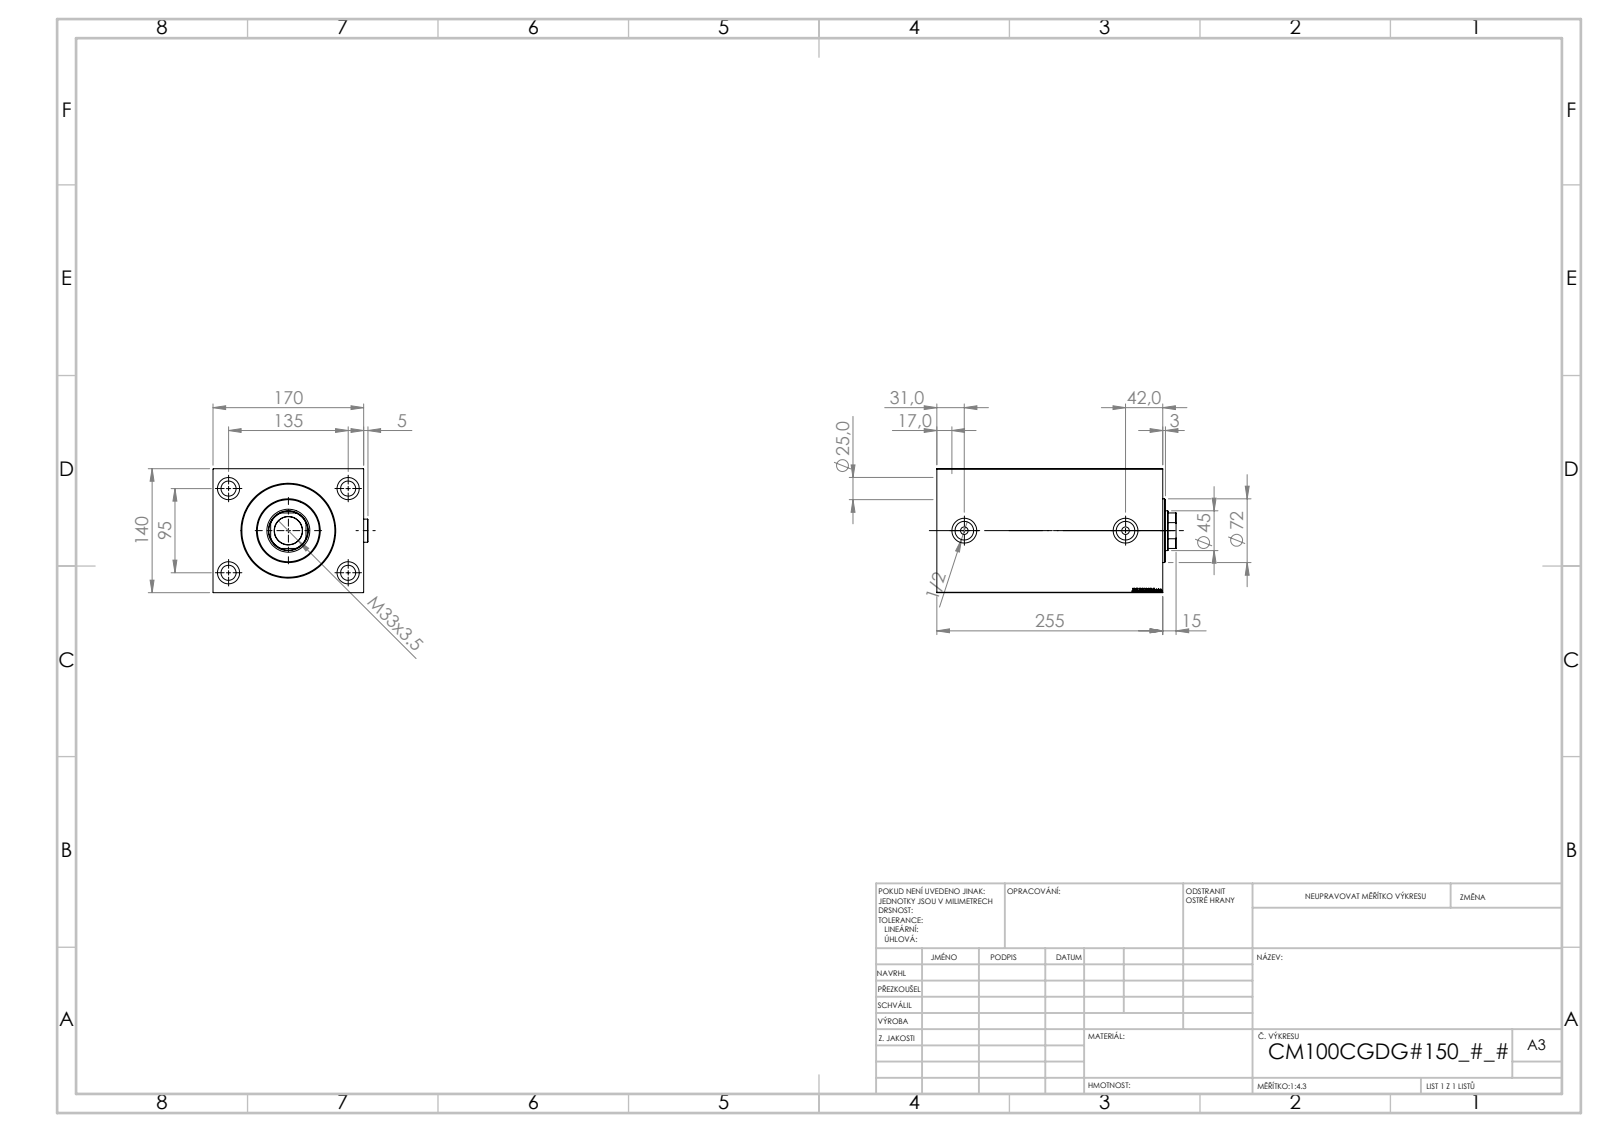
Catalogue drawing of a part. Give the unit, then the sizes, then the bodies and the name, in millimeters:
Units: millimetres
Overall size (bounding box): 270 × 174.9 × 140
Round holes (diameter × count): ⌀17 ×4, ⌀25 ×4, ⌀8.5 ×2, ⌀20.96 ×2, ⌀28 ×2, ⌀31.5 ×1, ⌀45 ×1, ⌀48.5 ×1, ⌀100 ×1, ⌀102 ×1, ⌀105 ×1
Round bosses / shafts (diameter × count): ⌀26 ×2, ⌀72 ×1
Partial cylindrical surfaces — rounded edges, fillets, slot ends (radius × count): R22 ×1
Main face-to-face distances: 140, 170, 255, 229, 26, 15, 214, 240, 90, 165
Hole centre spacings: 82.54, 95, 135, 165.08, 182
Volume: 4 841 000 mm³ · Surface area: 429 063 mm²
Bodies: 5 solids, 919 faces (443 planar, 78 cylindrical, 398 other)
Part name (STEP PRODUCT): Zatka_OIL_PORT; V450CM_C_VCP; V450CM_C_Body; V450CM_VC_B
STEP written by: SolidWorks 2019 (CONFIG_CONTROL_DESIGN)
